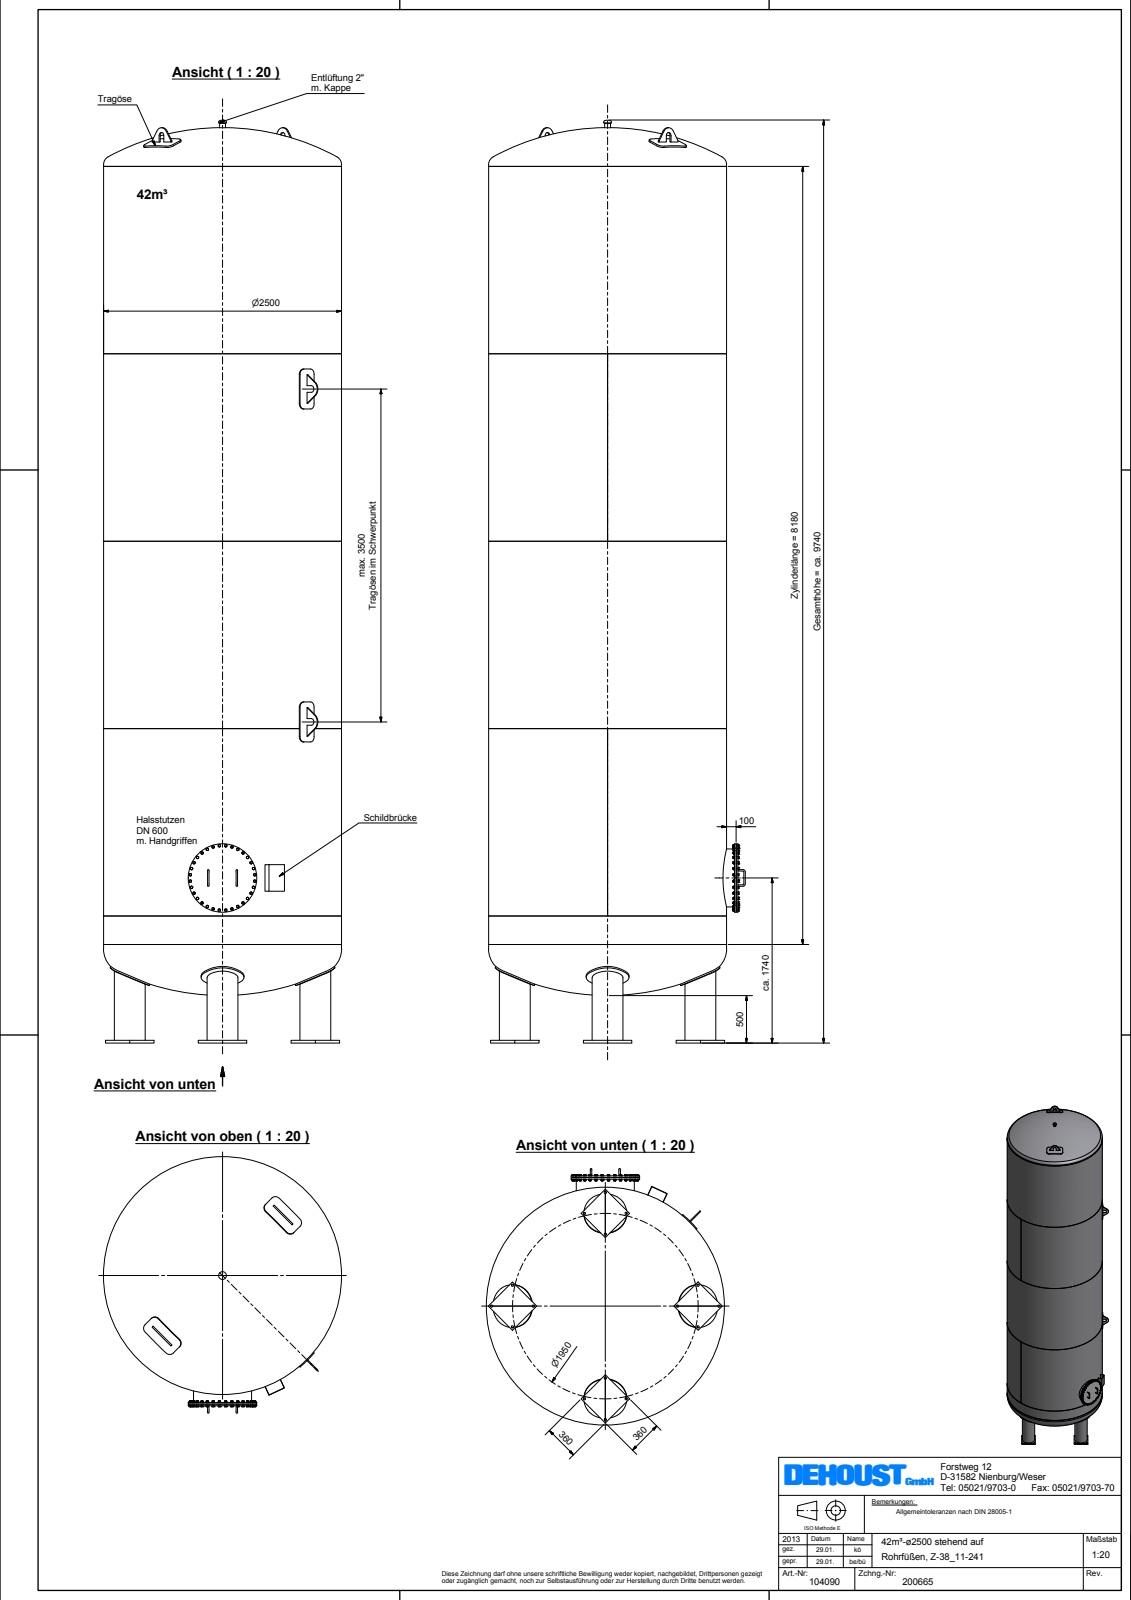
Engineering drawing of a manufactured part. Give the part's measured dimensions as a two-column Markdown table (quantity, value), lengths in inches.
| quantity | value |
| --- | --- |
| part name | Beh\\S\\dlter_Z-38_11-241_2500_042_KV |
| STEP written by | Autodesk Inventor 2012 (AUTOMOTIVE_DESIGN) |
| units | inches |
| bodies | 6 solids, 216 faces (125 planar, 61 cylindrical, 30 other) |
| overall size | 378.889 × 103.11 × 98.425 |
| volume | 143 500 in³ |
| surface area | 247 800 in² |
| round holes (diameter × count) | 7.874 × 4, 12.083 × 4, 2.374 × 1, 23.543 × 1, 97.638 × 1, 97.874 × 1, 97.953 × 1 |
| round bosses / shafts (diameter × count) | 17.717 × 4, 12.752 × 4, 98.425 × 1, 28.346 × 1, 24.016 × 1 |
| partial cylindrical surfaces (radius × count) | 2.205 × 16, 1.378 × 4, 3.346 × 4, 49.606 × 1 |
| main face-to-face distances | 40.809, 1.181, 39.628, 0.63, 14.171, 54.278, 0.116, 6.968, 0.115, 0.394 |
| hole center spacings | 38.386, 54.286, 76.772 |
